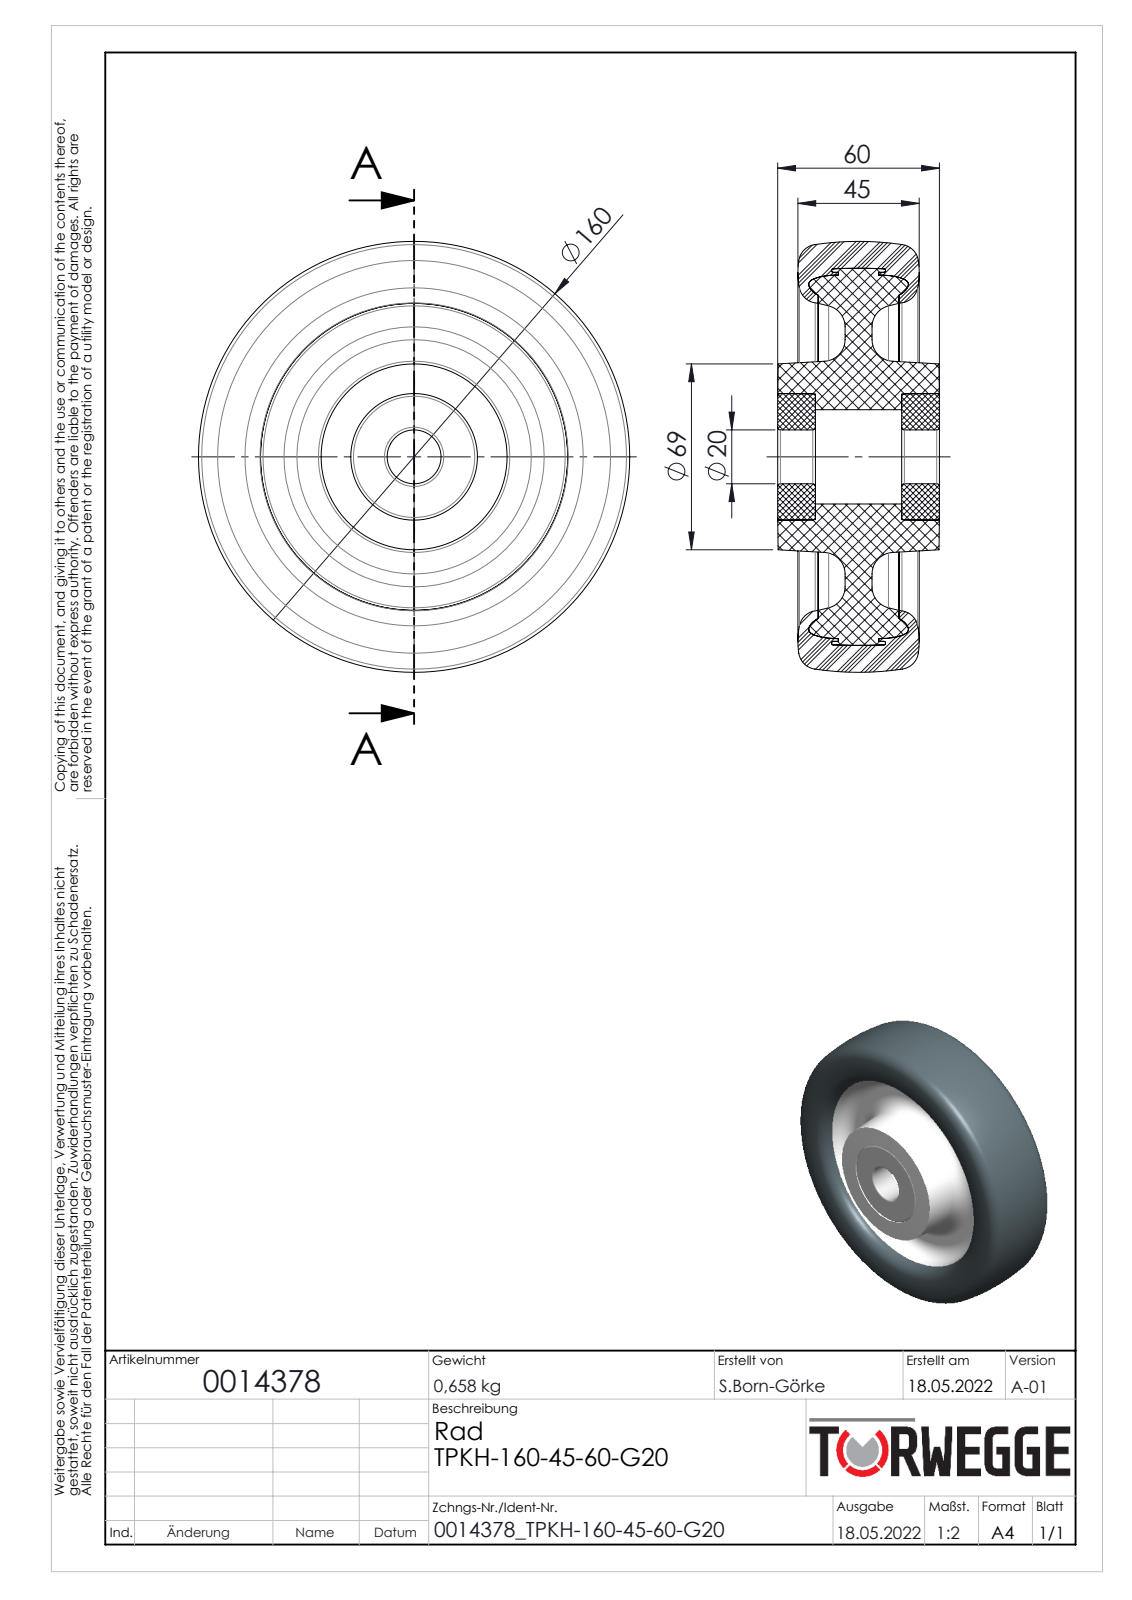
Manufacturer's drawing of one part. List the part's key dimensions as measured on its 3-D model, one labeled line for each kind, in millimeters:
Part name (STEP PRODUCT): 0014378
STEP written by: SolidWorks 2020 (AUTOMOTIVE_DESIGN)
Units: millimetres
Bodies: 0 solids, 66 faces (6 planar, 6 cylindrical, 54 other)
Overall size (bounding box): 160 × 159.97 × 60
Round holes (diameter × count): ⌀20 ×1, ⌀35 ×1
Main face-to-face distances: 10, 25, 35, 15, 45, 20, 60, 30
